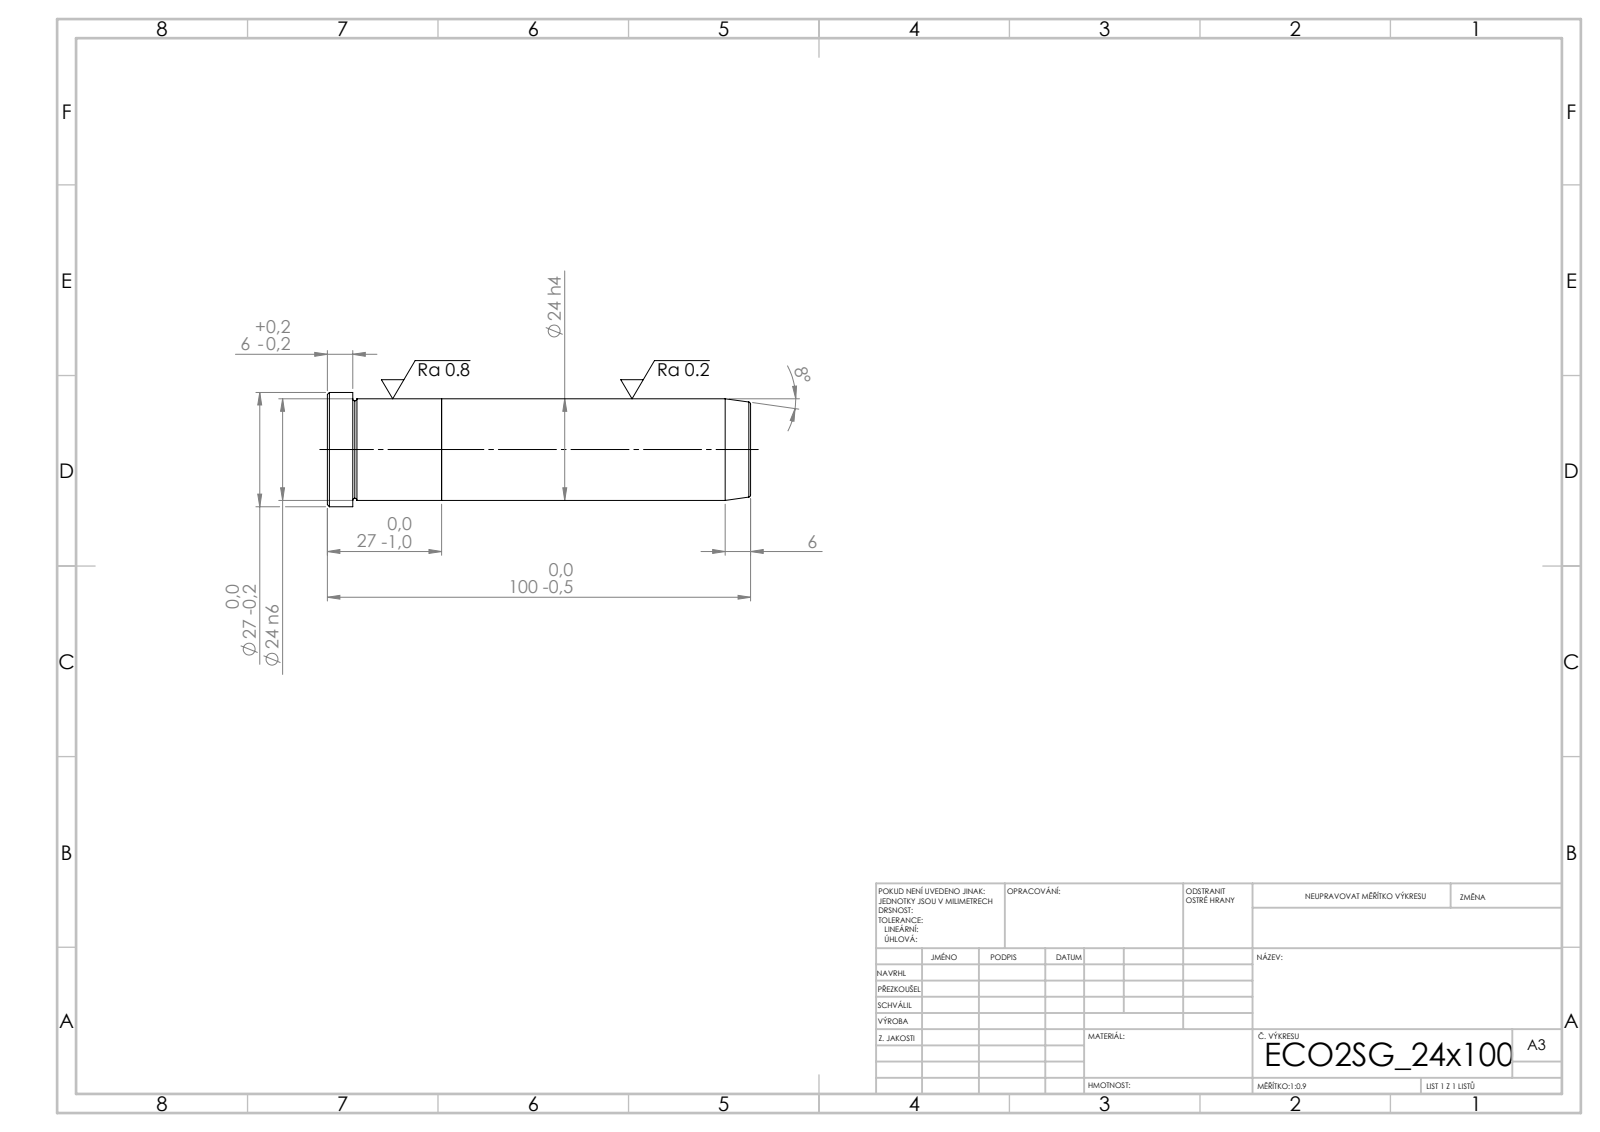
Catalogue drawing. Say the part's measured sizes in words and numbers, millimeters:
Its 3-D file was written by "SolidWorks 2019 (CONFIG_CONTROL_DESIGN)". It is 2 solids with 21 faces: 5 planar, 6 cylindrical and 10 other. Overall it measures 100 by 27 by 27 millimeters. Its volume is 45 731 cubic millimeters and its surface area 9 577 square millimeters. Round bosses or shafts: 1 of diameter 27, 1 of diameter 24. The main face-to-face distances are 27, 73, 100, 94, 21, 6.
